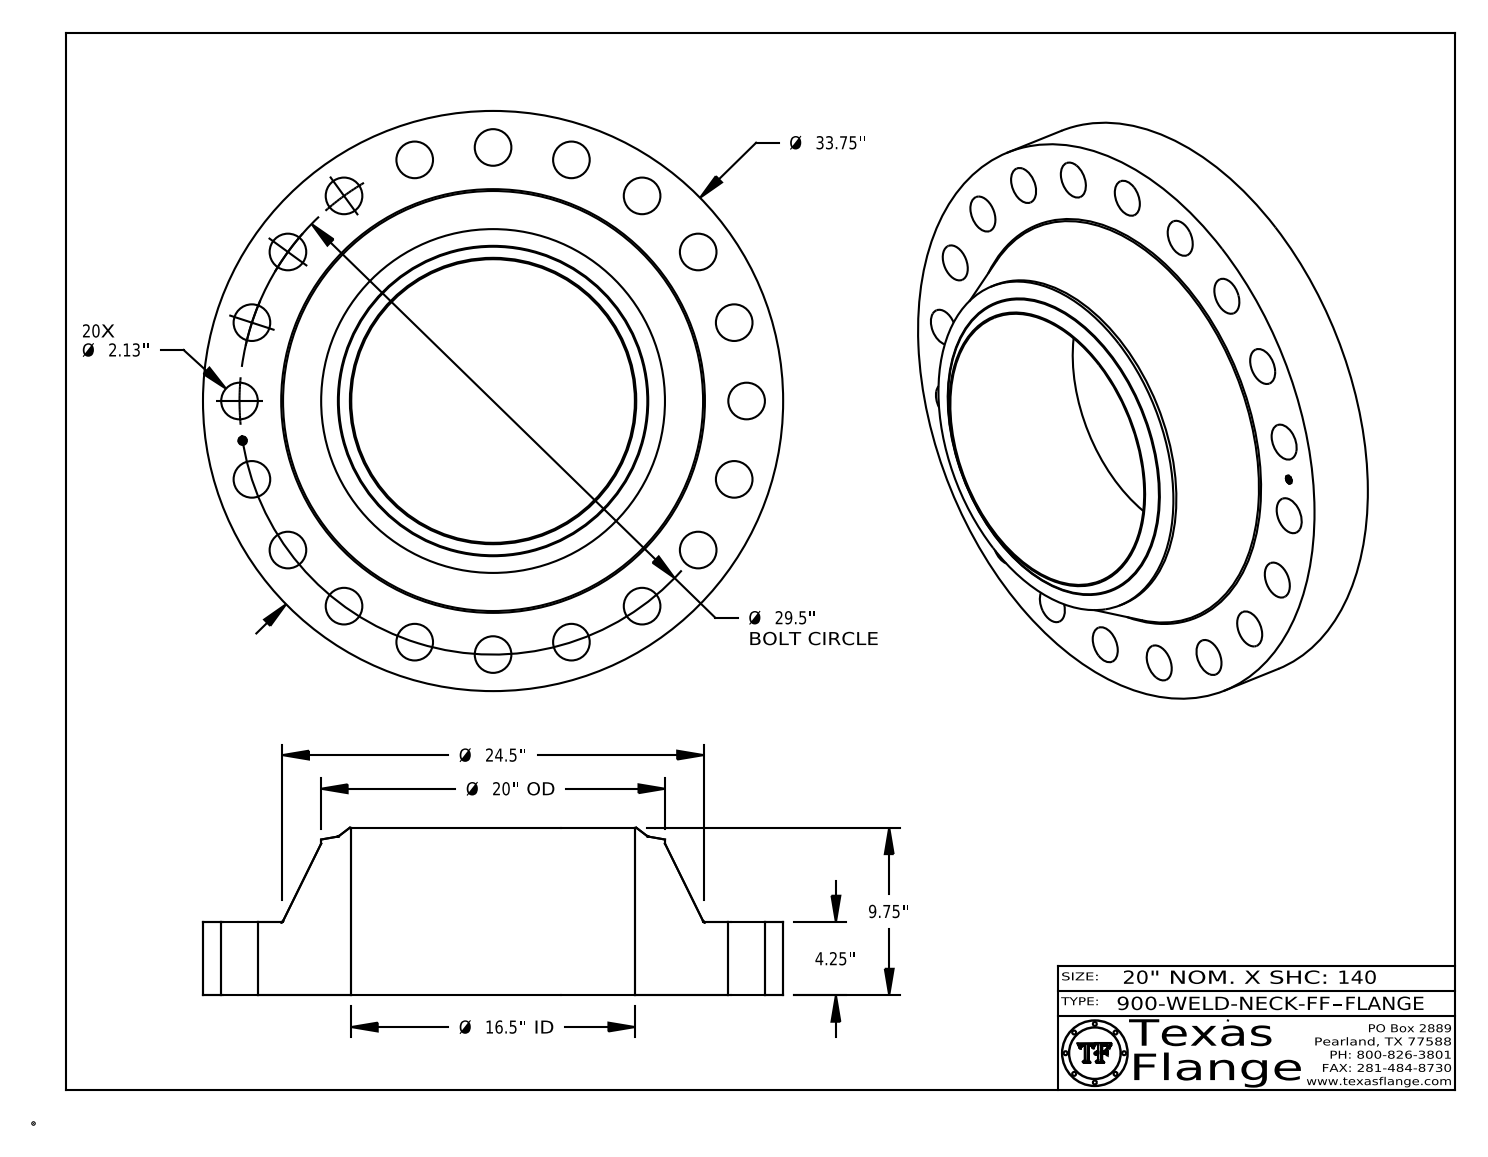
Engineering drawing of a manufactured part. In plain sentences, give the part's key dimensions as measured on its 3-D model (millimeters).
The part is named "900-WELD-NECK-FF". Its 3-D file was written by "CATIA V5 STEP AP214 (AUTOMOTIVE_DESIGN)". It is 1 solid with 444 faces: 368 planar, 66 cylindrical and 10 other. Overall it measures 857.3 by 857.3 by 247.7 millimeters. Its volume is 56 440 000 cubic millimeters and its surface area 1 914 000 square millimeters. Round holes: 20 of diameter 54.1, 1 of diameter 12.6, 1 of diameter 419.1. Round bosses or shafts: 8 of diameter 0.8, 1 of diameter 857.3, 1 of diameter 508, 1 of diameter 9.9. The main face-to-face distances are 108, 247.7, 139.7, 107.6, 0.4, 140.1, 3.8, 3.7, 0.7, 2.4. The hole center spacings are 374.7, 740.1, 117.2, 440.4, 529.8, 606.2, 667.6, 231.5.
